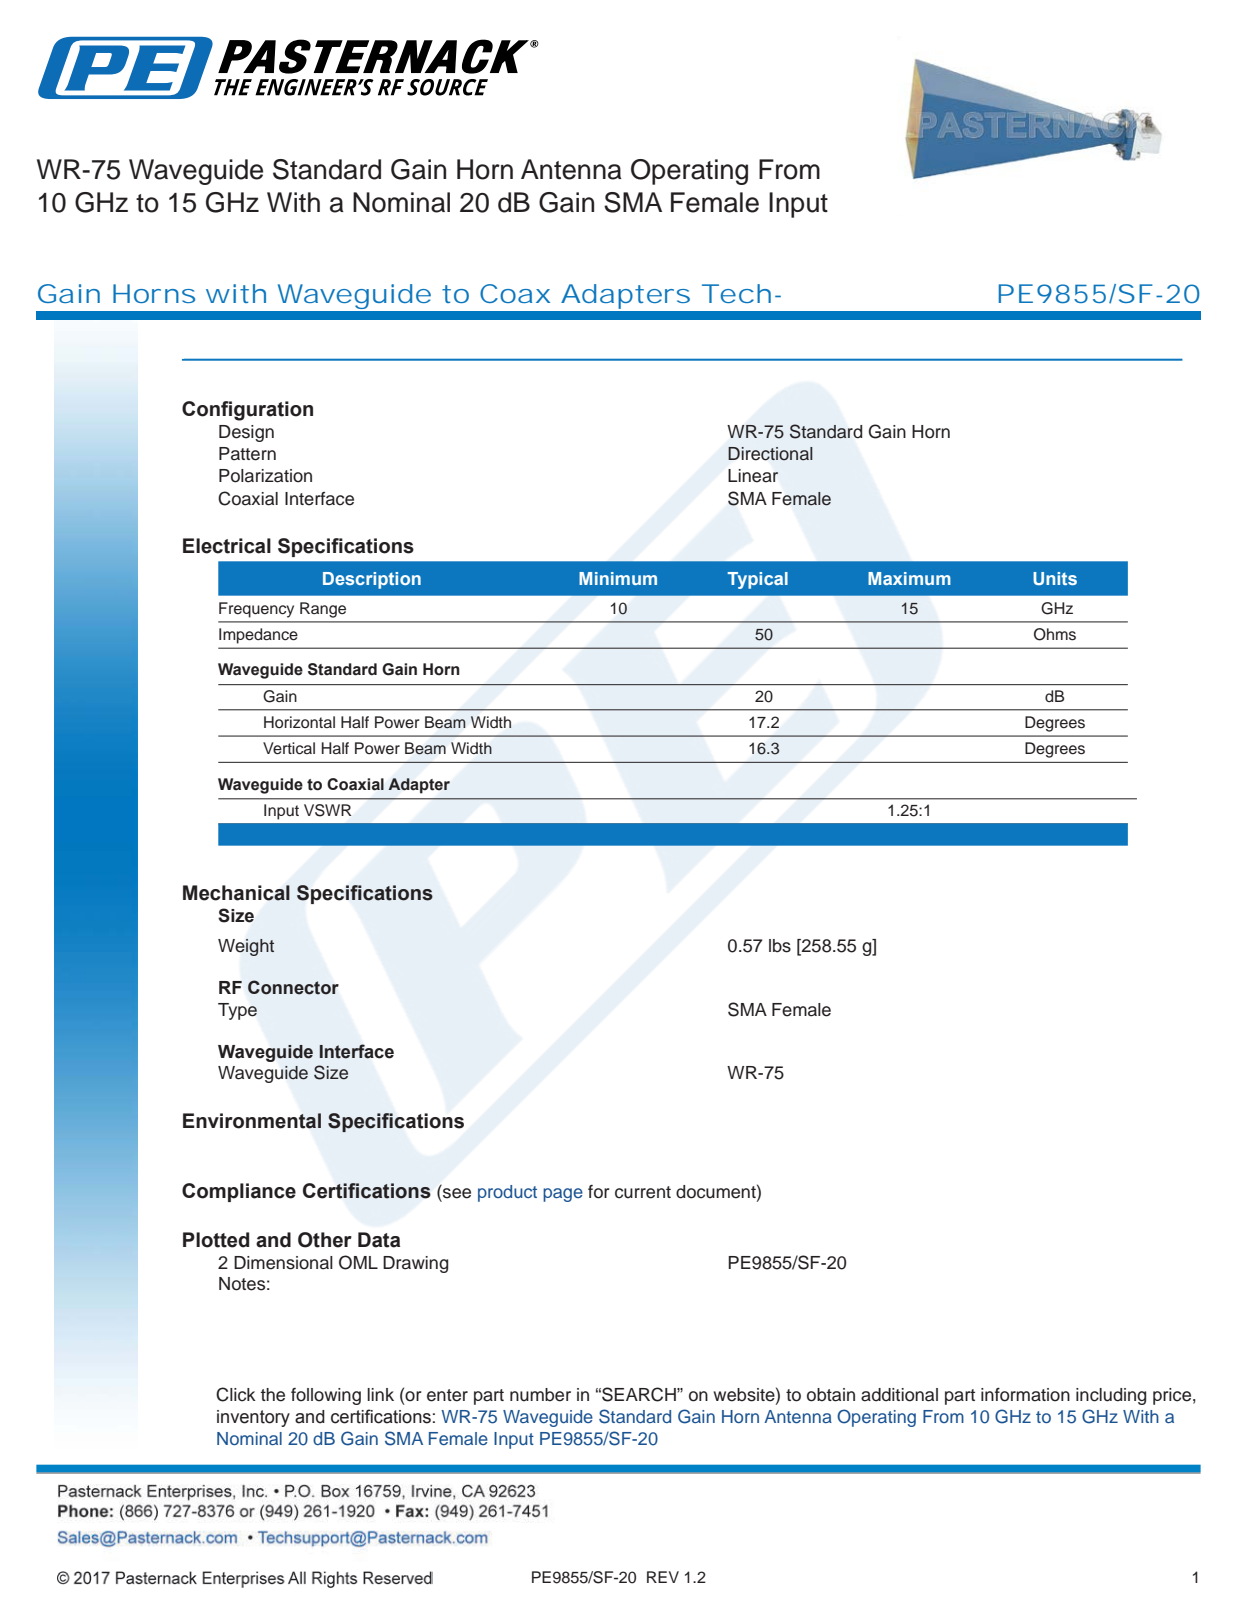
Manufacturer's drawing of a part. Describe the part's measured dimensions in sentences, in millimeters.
The part is named "PE9819; Copy of Hex Screw^PE9855-SF-20; PE9855-SF-20; PE9855-20". Its 3-D file was written by "SolidWorks 2018 (CONFIG_CONTROL_DESIGN)". It is 11 solids with 458 faces: 234 planar, 115 cylindrical and 109 other. Overall it measures 228.7 by 101.7 by 78.8 millimeters. Its volume is 87 030 cubic millimeters and its surface area 94 900 square millimeters. Round holes: 4 of diameter 1.5, 4 of diameter 3.7, 4 of diameter 3.7, 4 of diameter 4.1, 1 of diameter 1, 1 of diameter 1.3, 1 of diameter 4.6. Round bosses or shafts: 4 of diameter 7.1, 4 of diameter 7, 4 of diameter 4.3, 4 of diameter 3.6, 4 of diameter 3, 4 of diameter 1.9, 4 of diameter 1.3, 1 of diameter 6.4. Partial cylindrical surfaces (rounded edges, fillets, slot ends): 12 of radius 1.3, 4 of radius 0.9. The main face-to-face distances are 1.6, 1.6, 6.4, 38.1, 4.9, 11.3, 2.6, 12.1, 9.5, 9.5. The hole center spacings are 26.4, 6.6, 6.7, 9.4, 9.4, 13.3, 28.4, 28.5.
